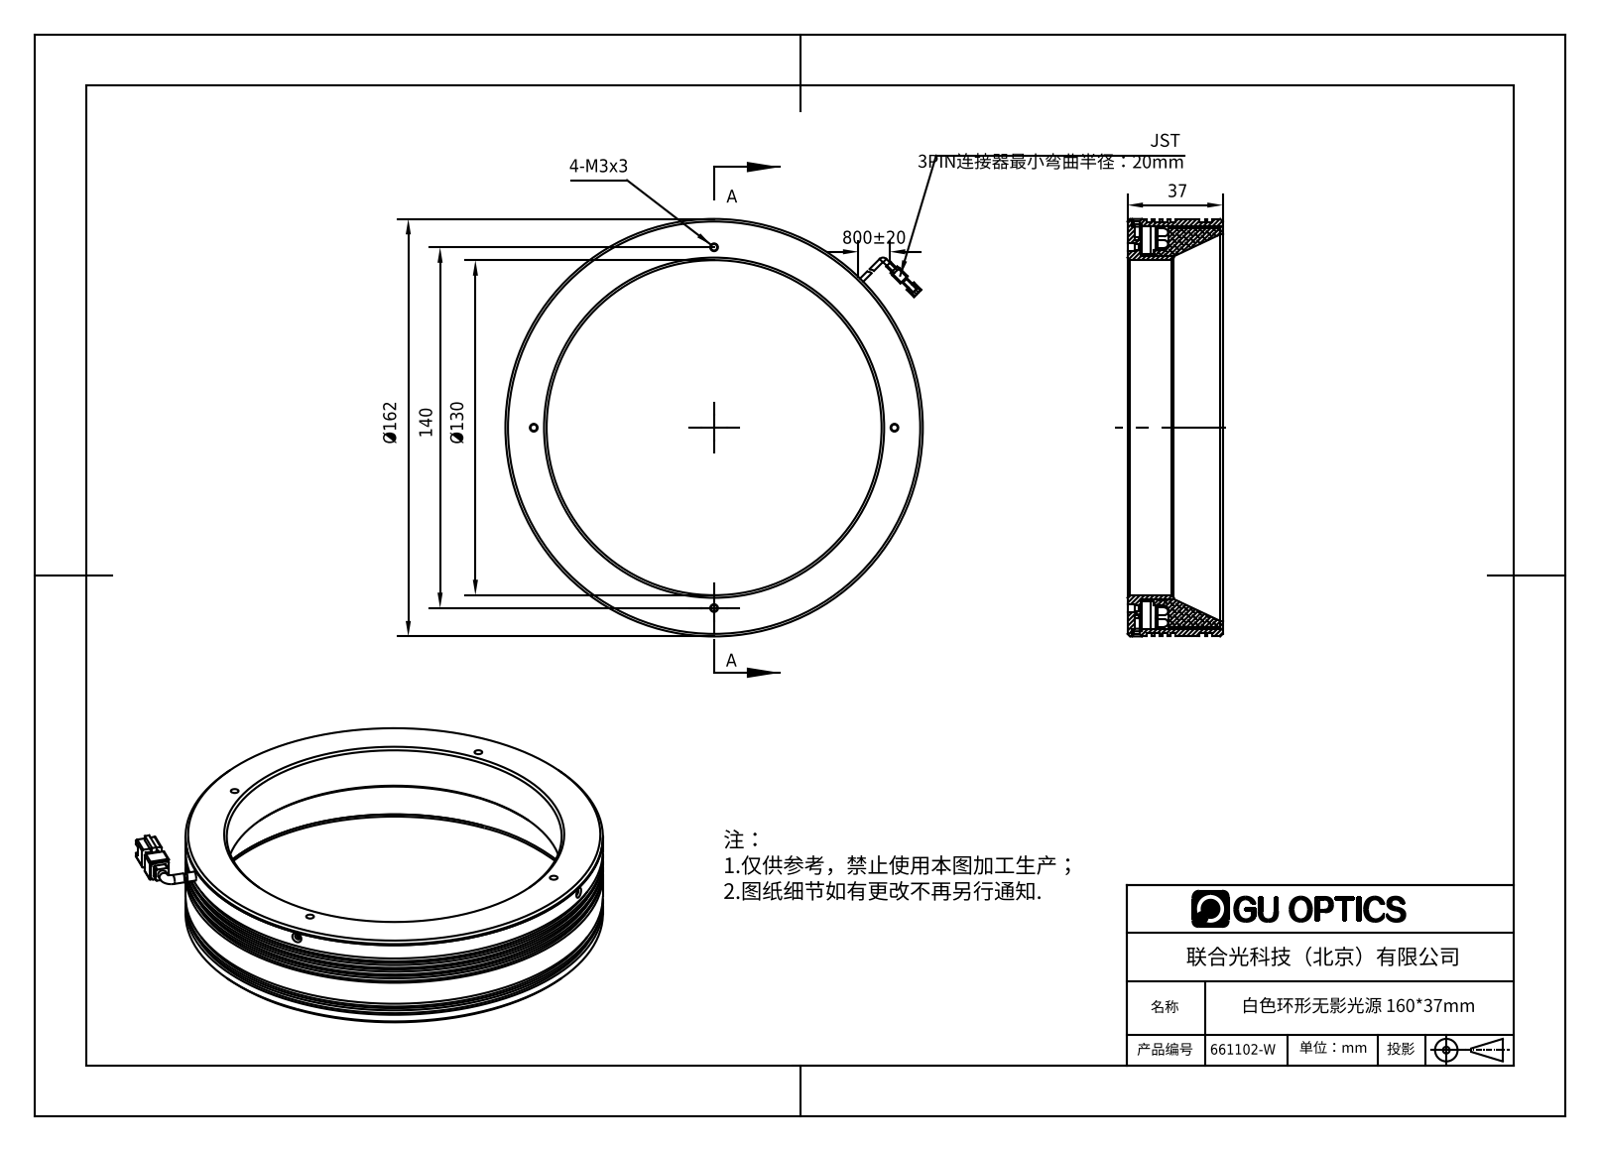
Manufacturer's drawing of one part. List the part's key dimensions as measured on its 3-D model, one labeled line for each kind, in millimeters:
Part name (STEP PRODUCT): 661102-W
STEP written by: SolidWorks 2016 (AUTOMOTIVE_DESIGN)
Units: millimetres
Bodies: 5 solids, 260 faces (91 planar, 129 cylindrical, 40 other)
Overall size (bounding box): 168.11 × 162 × 38.5
Volume: 159 756 mm³ · Surface area: 113 568 mm²
Round holes (diameter × count): ⌀2.5 ×4, ⌀3 ×4, ⌀1.6 ×2, ⌀2 ×2, ⌀2.4 ×2, ⌀130 ×1, ⌀133 ×1, ⌀150 ×1, ⌀158 ×1
Round bosses / shafts (diameter × count): ⌀3.5 ×2, ⌀162 ×1, ⌀159.6 ×1, ⌀156 ×1, ⌀155 ×1, ⌀138 ×1, ⌀135 ×1
Partial cylindrical surfaces — rounded edges, fillets, slot ends (radius × count): R0.5 ×8, R1 ×4, R6 ×1
Main face-to-face distances: 5, 3, 14.5, 6, 1, 11, 2, 3.5, 20.5, 20
Hole centre spacings: 70, 98.99, 140
